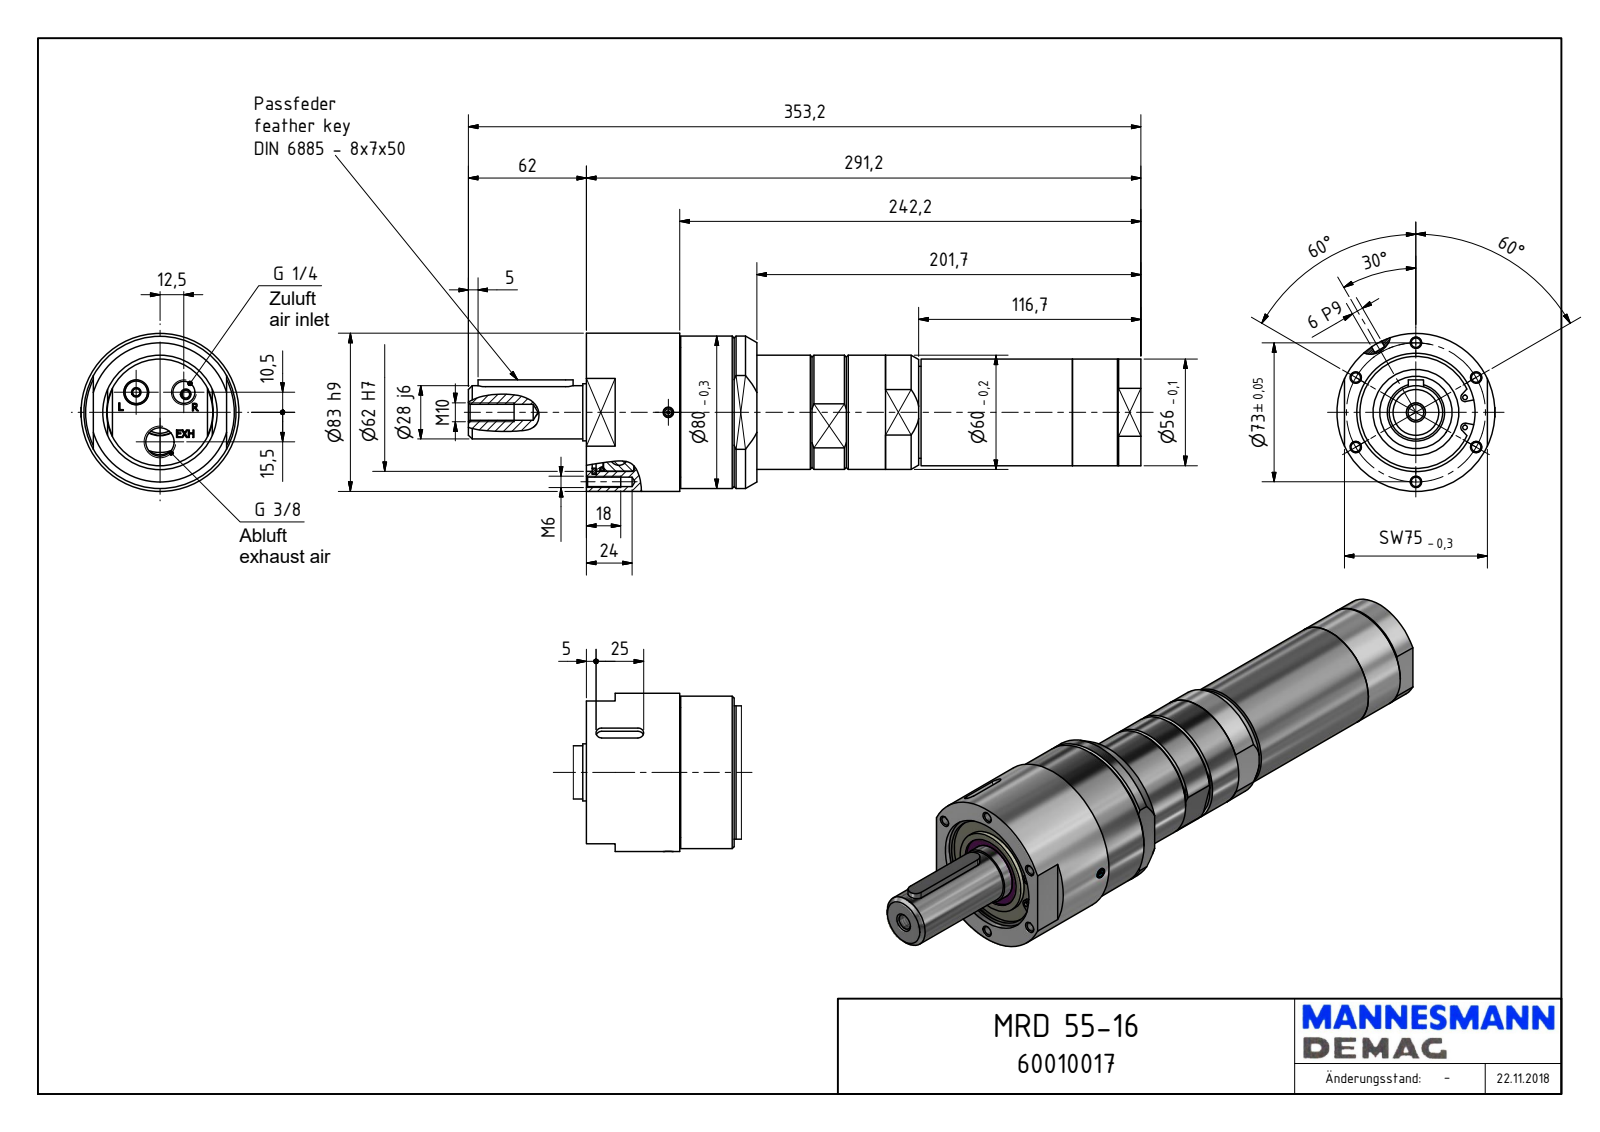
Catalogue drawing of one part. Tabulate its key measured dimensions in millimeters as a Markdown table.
| quantity | value |
| --- | --- |
| part name | MRD 55-16_60010017 |
| STEP written by | Autodesk Inventor 2018 (AUTOMOTIVE_DESIGN) |
| units | millimeters |
| bodies | 1 solid, 338 faces (168 planar, 98 cylindrical, 72 other) |
| overall size | 353.2 × 83 × 83 |
| volume | 999 674 mm³ |
| surface area | 100 073 mm² |
| round holes (diameter × count) | 4.92 × 6, 1.55 × 3, 4 × 3, 2.5 × 2, 5.5 × 2, 8.38 × 1, 11.45 × 1, 14.95 × 1, 36.5 × 1, 38 × 1, 40 × 1, 58.69 × 1 |
| round bosses / shafts (diameter × count) | 5 × 2, 3.6 × 2, 83 × 1, 80 × 1, 68.18 × 1, 67 × 1, 60 × 1, 56 × 1 |
| partial cylindrical surfaces (radius × count) | 10 × 6, 2.25 × 2, 3 × 2, 4 × 2, 6 × 2, 5.72 × 1, 19.4 × 1, 21.8 × 1 |
| main face-to-face distances | 2.5, 49, 291.2, 242.2, 0.5, 10, 62.5, 201.7, 89.5, 40.5 |
| hole center spacings | 36.5, 63.22, 28.85, 73, 11.89, 16.32, 20.62, 26.77 |
